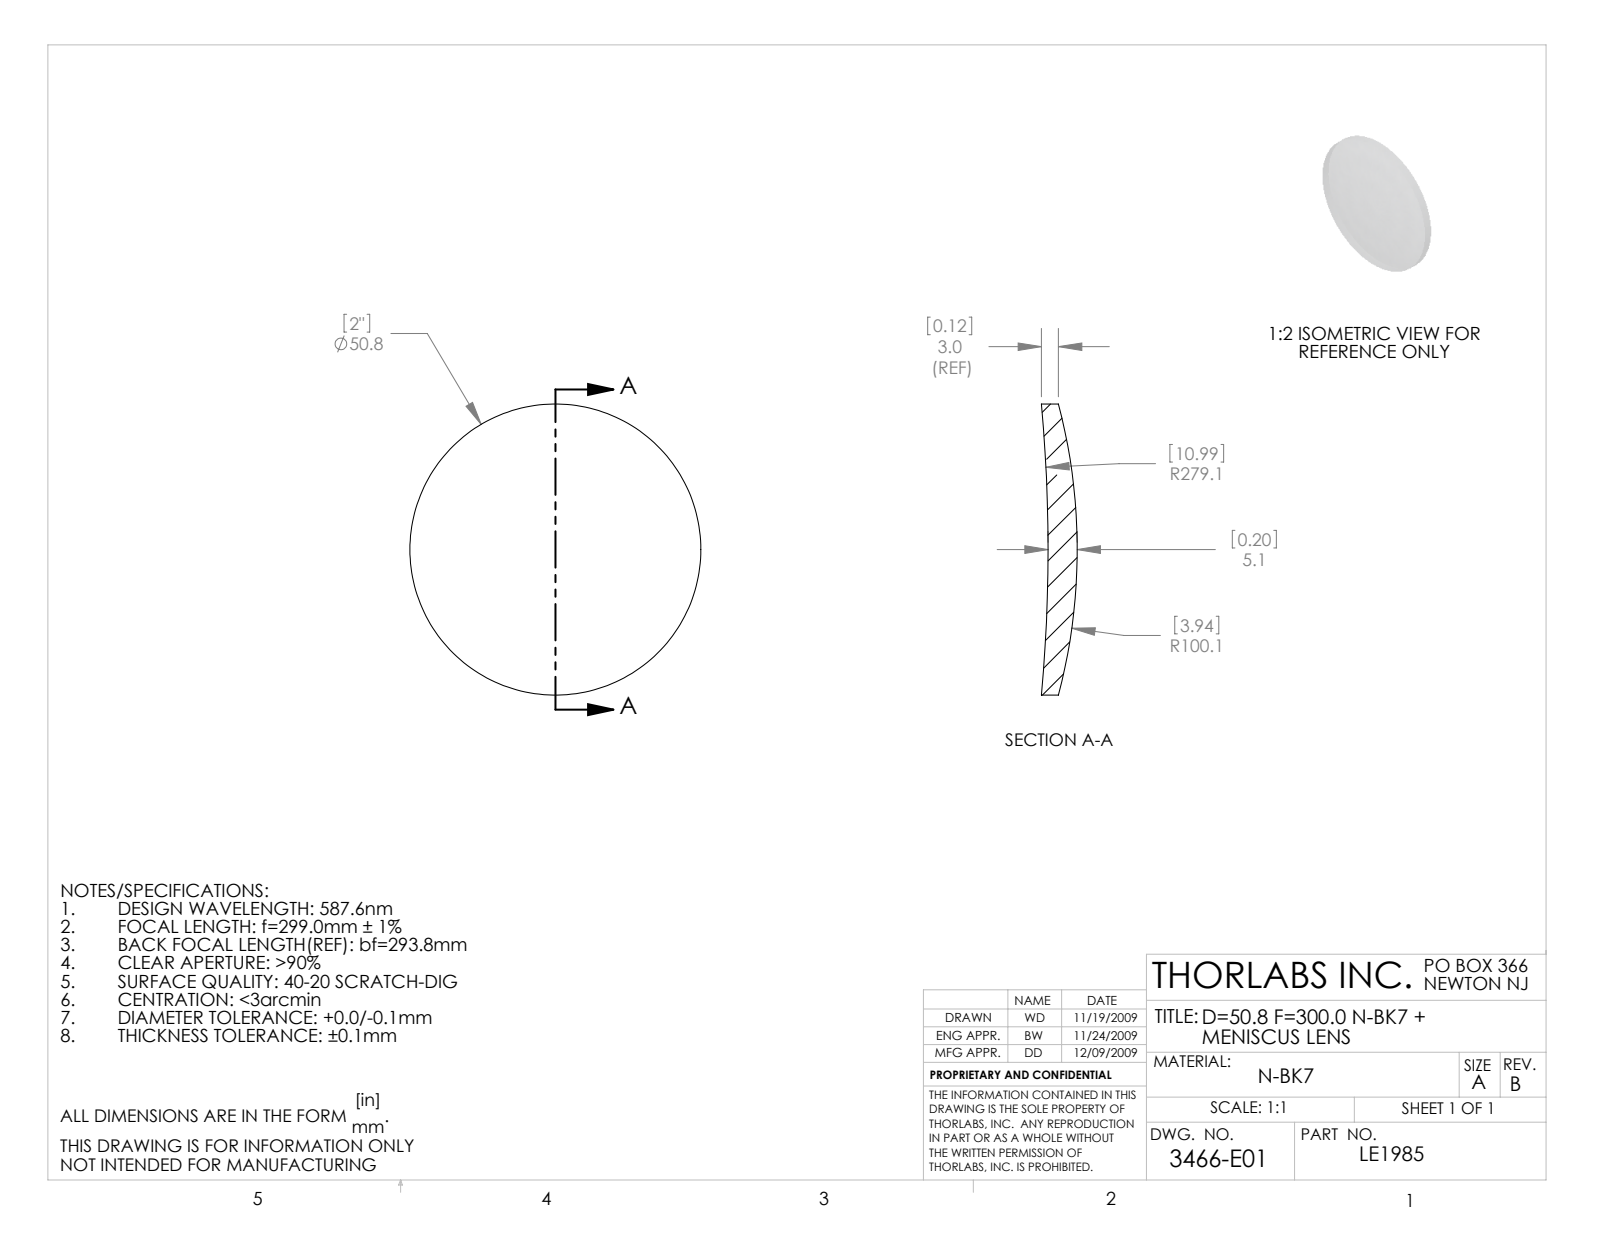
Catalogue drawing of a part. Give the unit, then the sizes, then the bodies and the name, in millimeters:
Units: millimetres
Overall size (bounding box): 50.8 × 50.8 × 6.26
Round bosses / shafts (diameter × count): ⌀50.8 ×1
Volume: 8 207 mm³ · Surface area: 4 567 mm²
Bodies: 1 solid, 6 faces (0 planar, 2 cylindrical, 4 other)
Part name (STEP PRODUCT): 3466-E0W
STEP written by: SolidWorks 2009 (AUTOMOTIVE_DESIGN)
